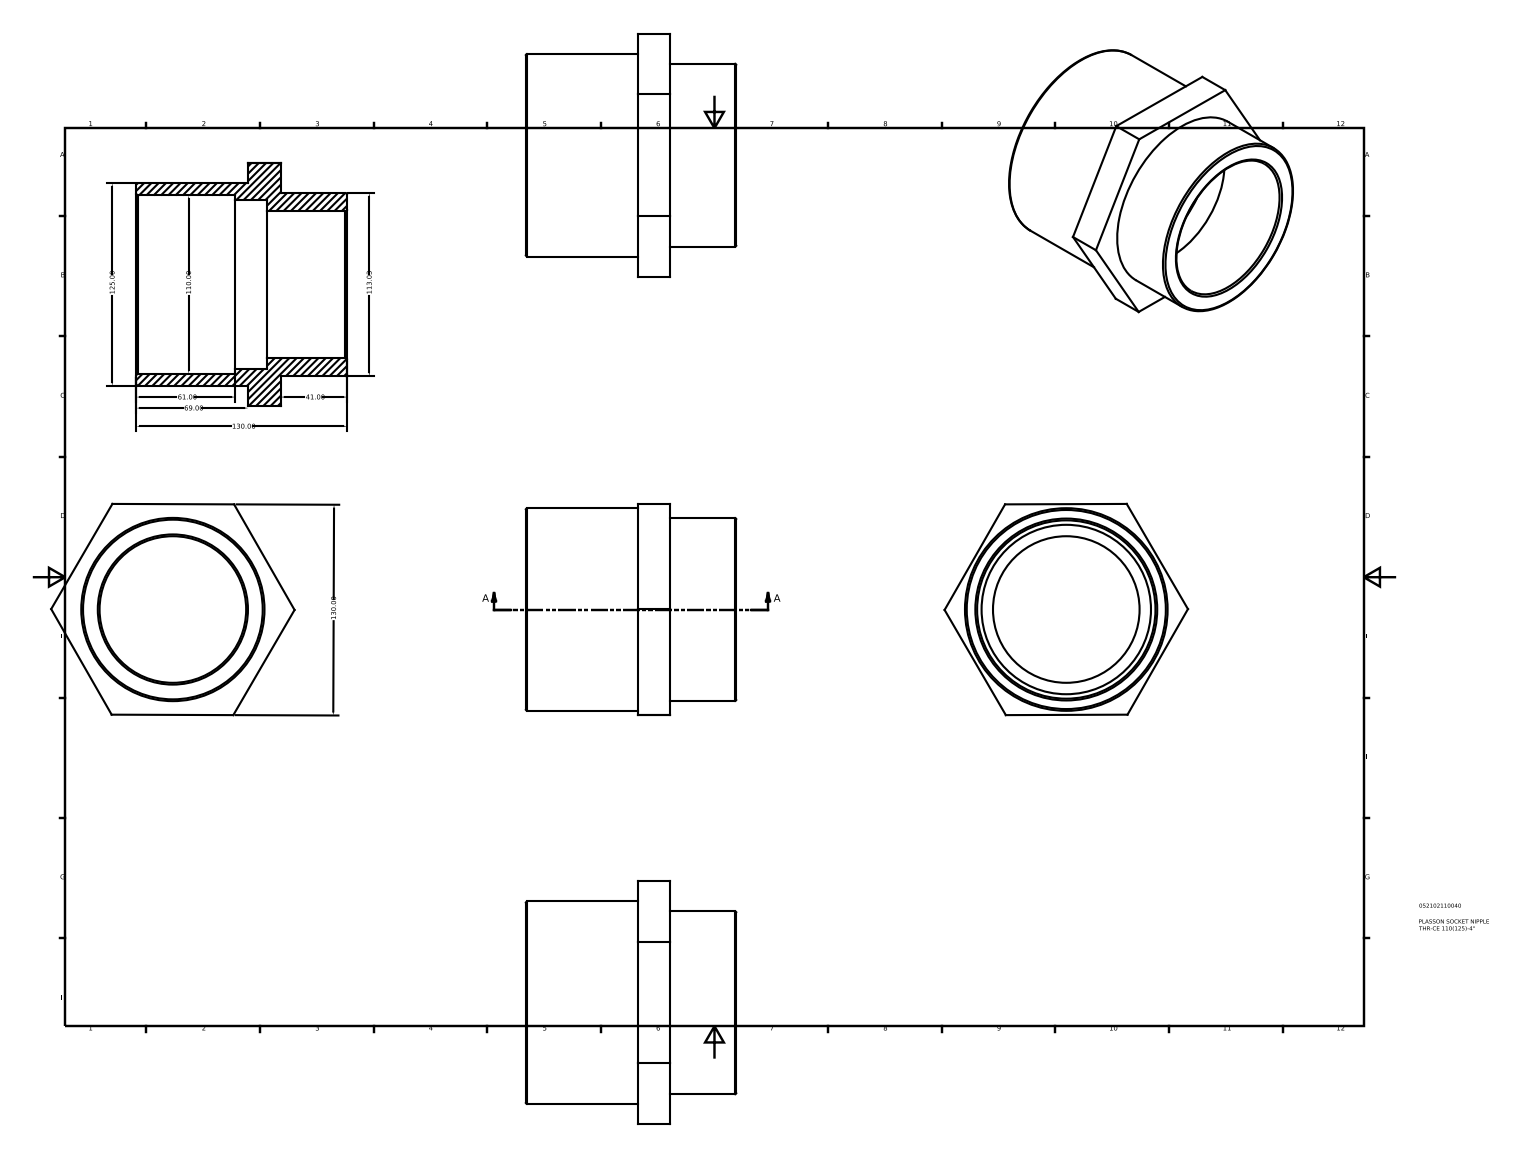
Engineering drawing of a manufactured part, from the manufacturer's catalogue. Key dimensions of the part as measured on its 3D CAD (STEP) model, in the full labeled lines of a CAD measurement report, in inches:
Part name (STEP PRODUCT): 052102110040
STEP written by: Autodesk Inventor 2015 (AUTOMOTIVE_DESIGN)
Units: inches
Bodies: 1 solid, 21 faces (12 planar, 5 cylindrical, 4 other)
Overall size (bounding box): 5.91 × 5.129 × 5.118
Volume: 29.6 in³ · Surface area: 167.4 in²
Round holes (diameter × count): ⌀3.56 ×1, ⌀4.114 ×1, ⌀4.331 ×1
Round bosses / shafts (diameter × count): ⌀4.921 ×1, ⌀4.45 ×1
Main face-to-face distances: 2.402, 1.614, 2.717, 0.787, 0.465, 0.323, 1.937, 3.181, 3.504, 5.118
